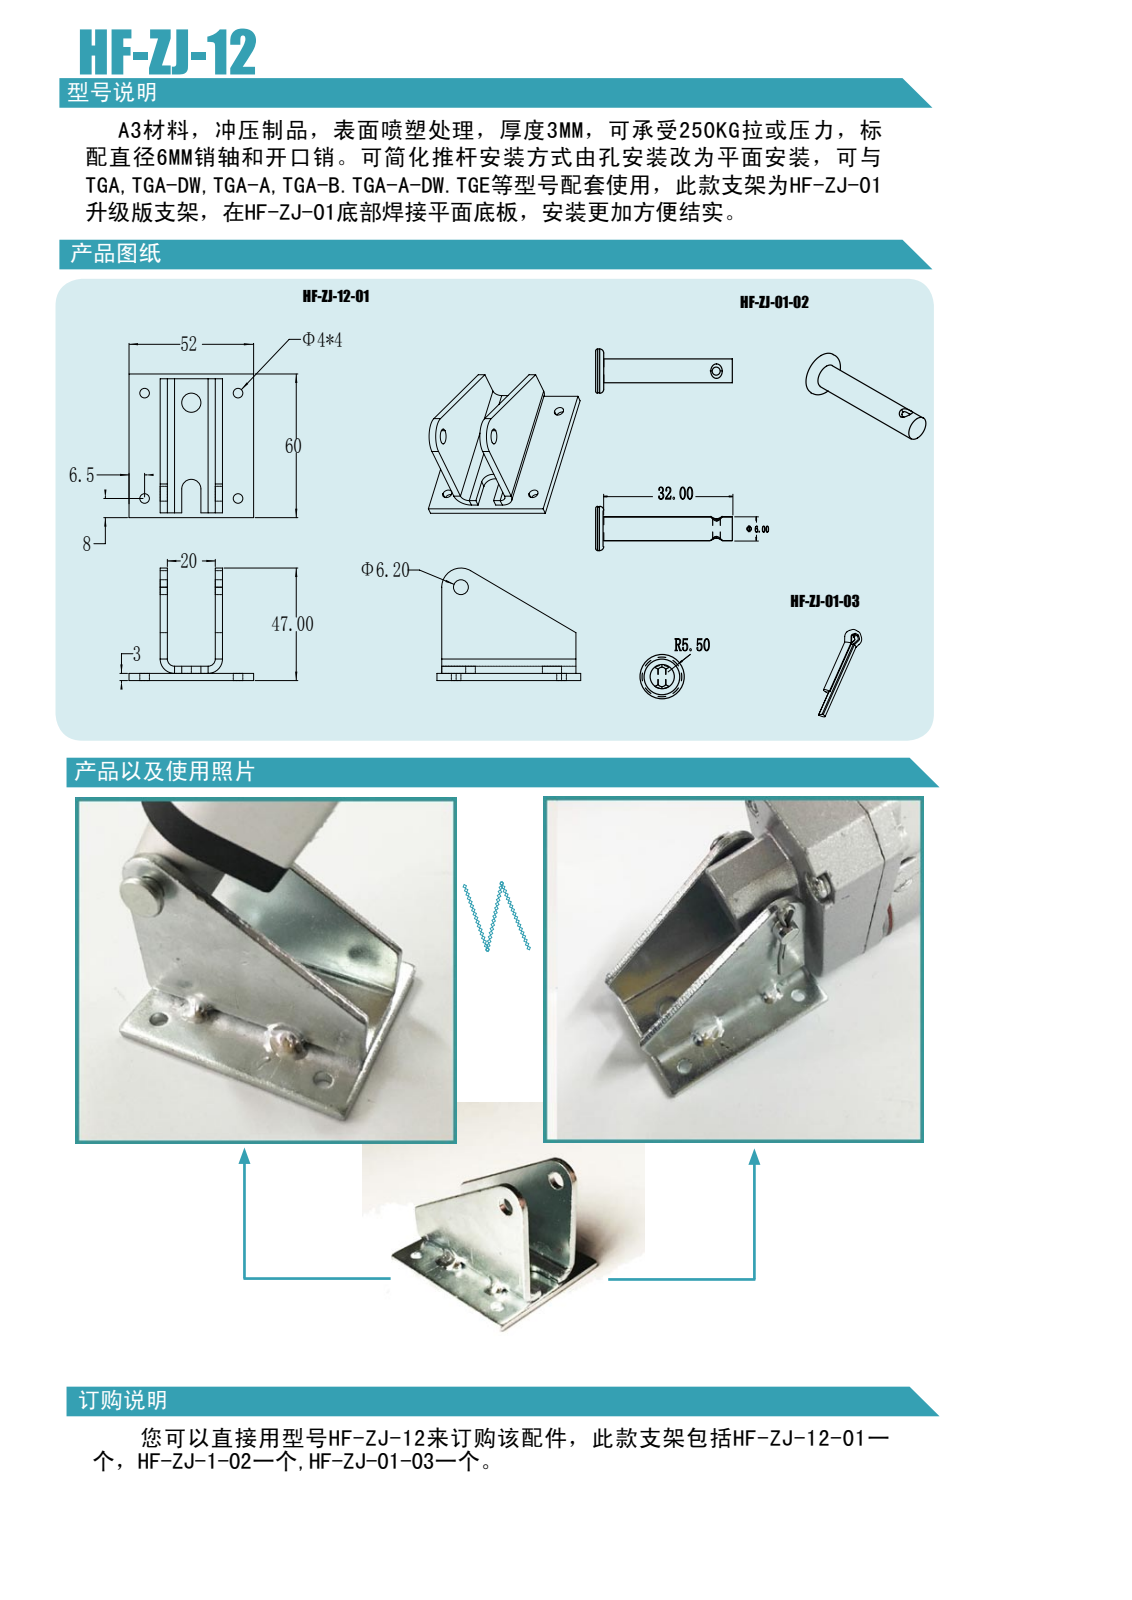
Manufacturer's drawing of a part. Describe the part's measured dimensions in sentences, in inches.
The part is named "ZJ-12". Its 3-D file was written by "PRO/ENGINEER BY PARAMETRIC TECHNOLOGY CORPORATION, 2008380 (CONFIG_CONTROL_DESIGN)". It is 2 solids with 48 faces: 27 planar, 21 cylindrical and 0 other. Overall it measures 60 by 52 by 47 inches. Its volume is 22 261 cubic inches and its surface area 16 751 square inches. Round holes: 4 of diameter 4, 1 of diameter 6.2, 1 of diameter 8. Partial cylindrical surfaces (rounded edges, fillets, slot ends): 2 of radius 3, 2 of radius 6, 1 of radius 4, 1 of radius 8. The main face-to-face distances are 3, 23, 26, 20, 6, 13, 16, 36, 39, 2. The hole center spacings are 19.906, 39, 44, 44.5, 58.796.
